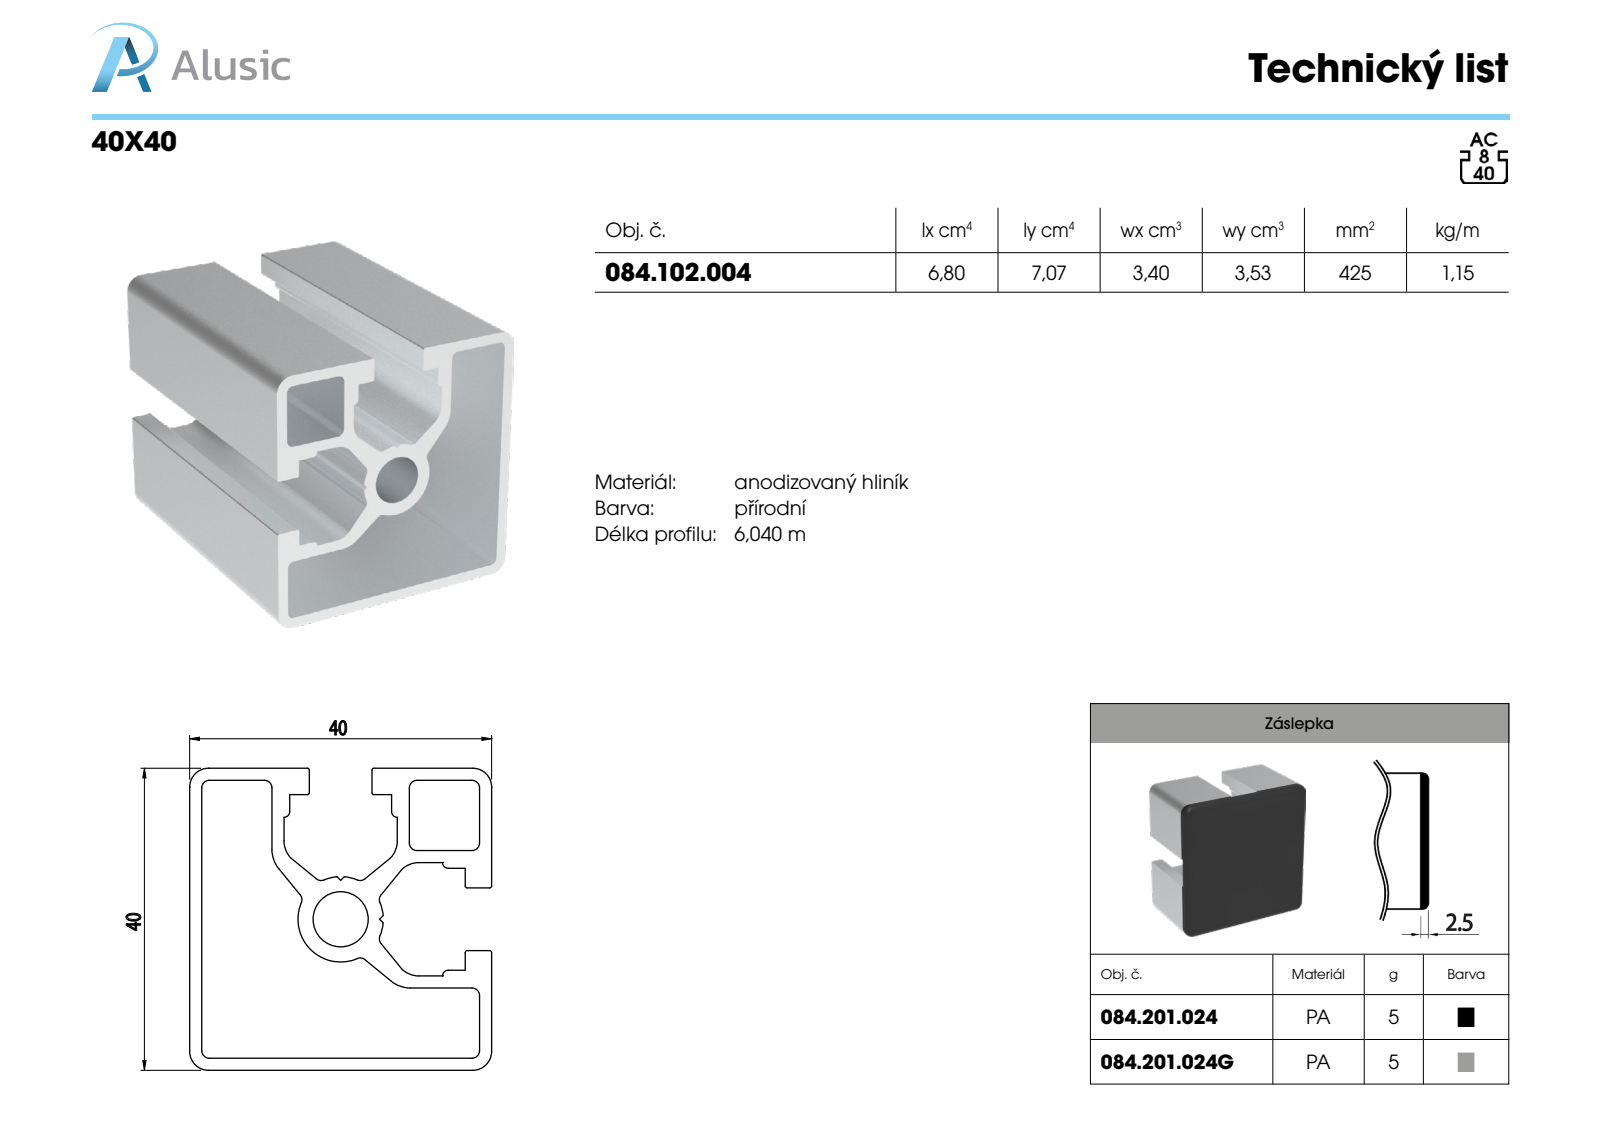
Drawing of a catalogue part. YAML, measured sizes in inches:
part_name: "084.102.004"
step_written_by: "SolidWorks 2011 (CONFIG_CONTROL_DESIGN)"
units: inches
bodies: {solids: 1, faces: 91, planar: 44, cylindrical: 47, other: 0}
overall_size: [3.937, 1.575, 1.575]
volume: 2.552
surface_area: 67.53
round_holes:
  - {diameter: 0.287, count: 1}
partial_cylinders:
  - {radius: 0.039, count: 15}
  - {radius: 0.01, count: 8}
  - {radius: 0.03, count: 4}
  - {radius: 0.098, count: 4}
  - {radius: 0.126, count: 4}
  - {radius: 0.157, count: 2}
  - {radius: 0.222, count: 1}
face_to_face_distances: [0.063, 1.512, 0.429, 1.575, 1.083, 1.146, 0.366, 1.449, 0.522, 0.459]
